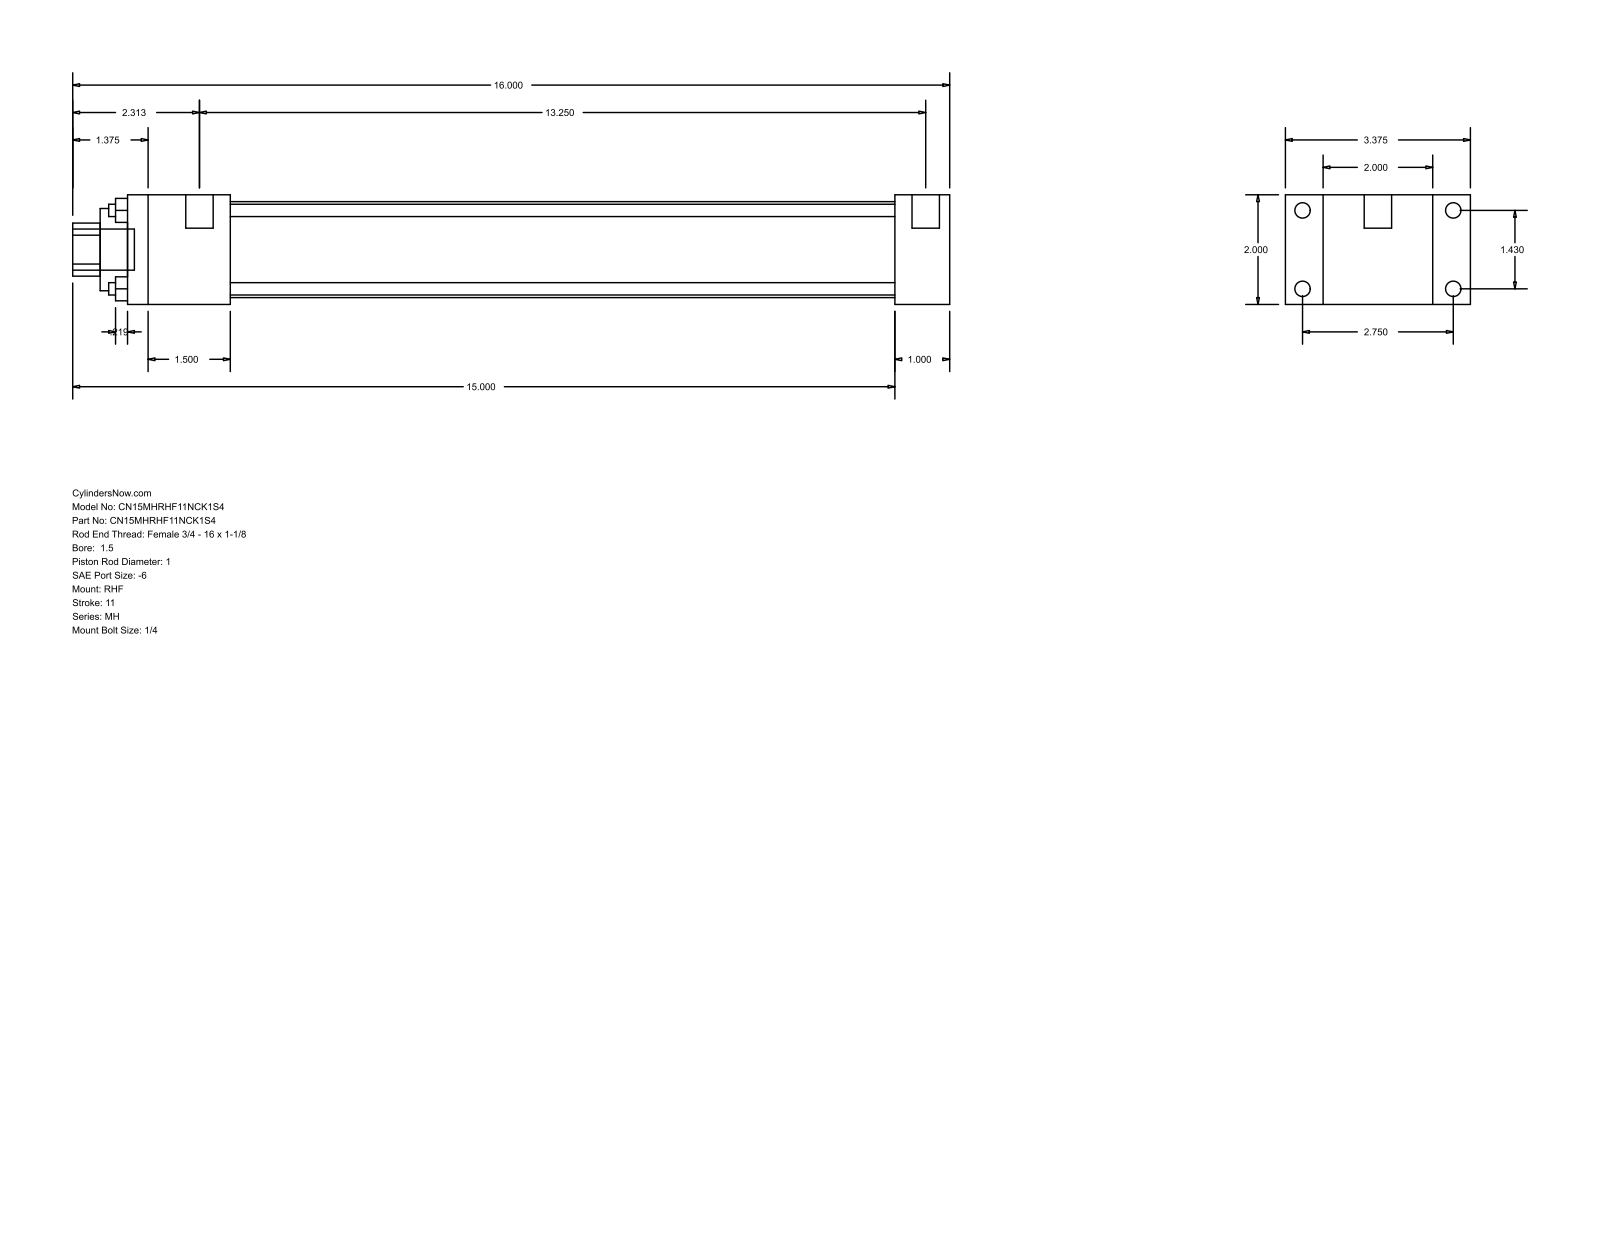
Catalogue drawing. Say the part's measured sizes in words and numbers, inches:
The part is named "MH_RHF__0150_1". Its 3-D file was written by "GSSL Pune (CONFIG_CONTROL_DESIGN)". It is 0 solids with 88 faces: 60 planar, 28 cylindrical and 0 other. Overall it measures 16 by 3.375 by 2 inches. Round holes: 4 of diameter 0.225, 1 of diameter 1, 1 of diameter 1.5, 1 of diameter 1.75. Round bosses or shafts: 4 of diameter 0.281, 4 of diameter 0.219, 2 of diameter 0.5, 1 of diameter 0.75. Partial cylindrical surfaces (rounded edges, fillets, slot ends): 1 of radius 0.484. The main face-to-face distances are 2, 1, 0.687, 2.687, 3.375, 15, 14, 1.875, 12.125, 13.125. The hole center spacings are 1.011, 1.43, 2.022.
